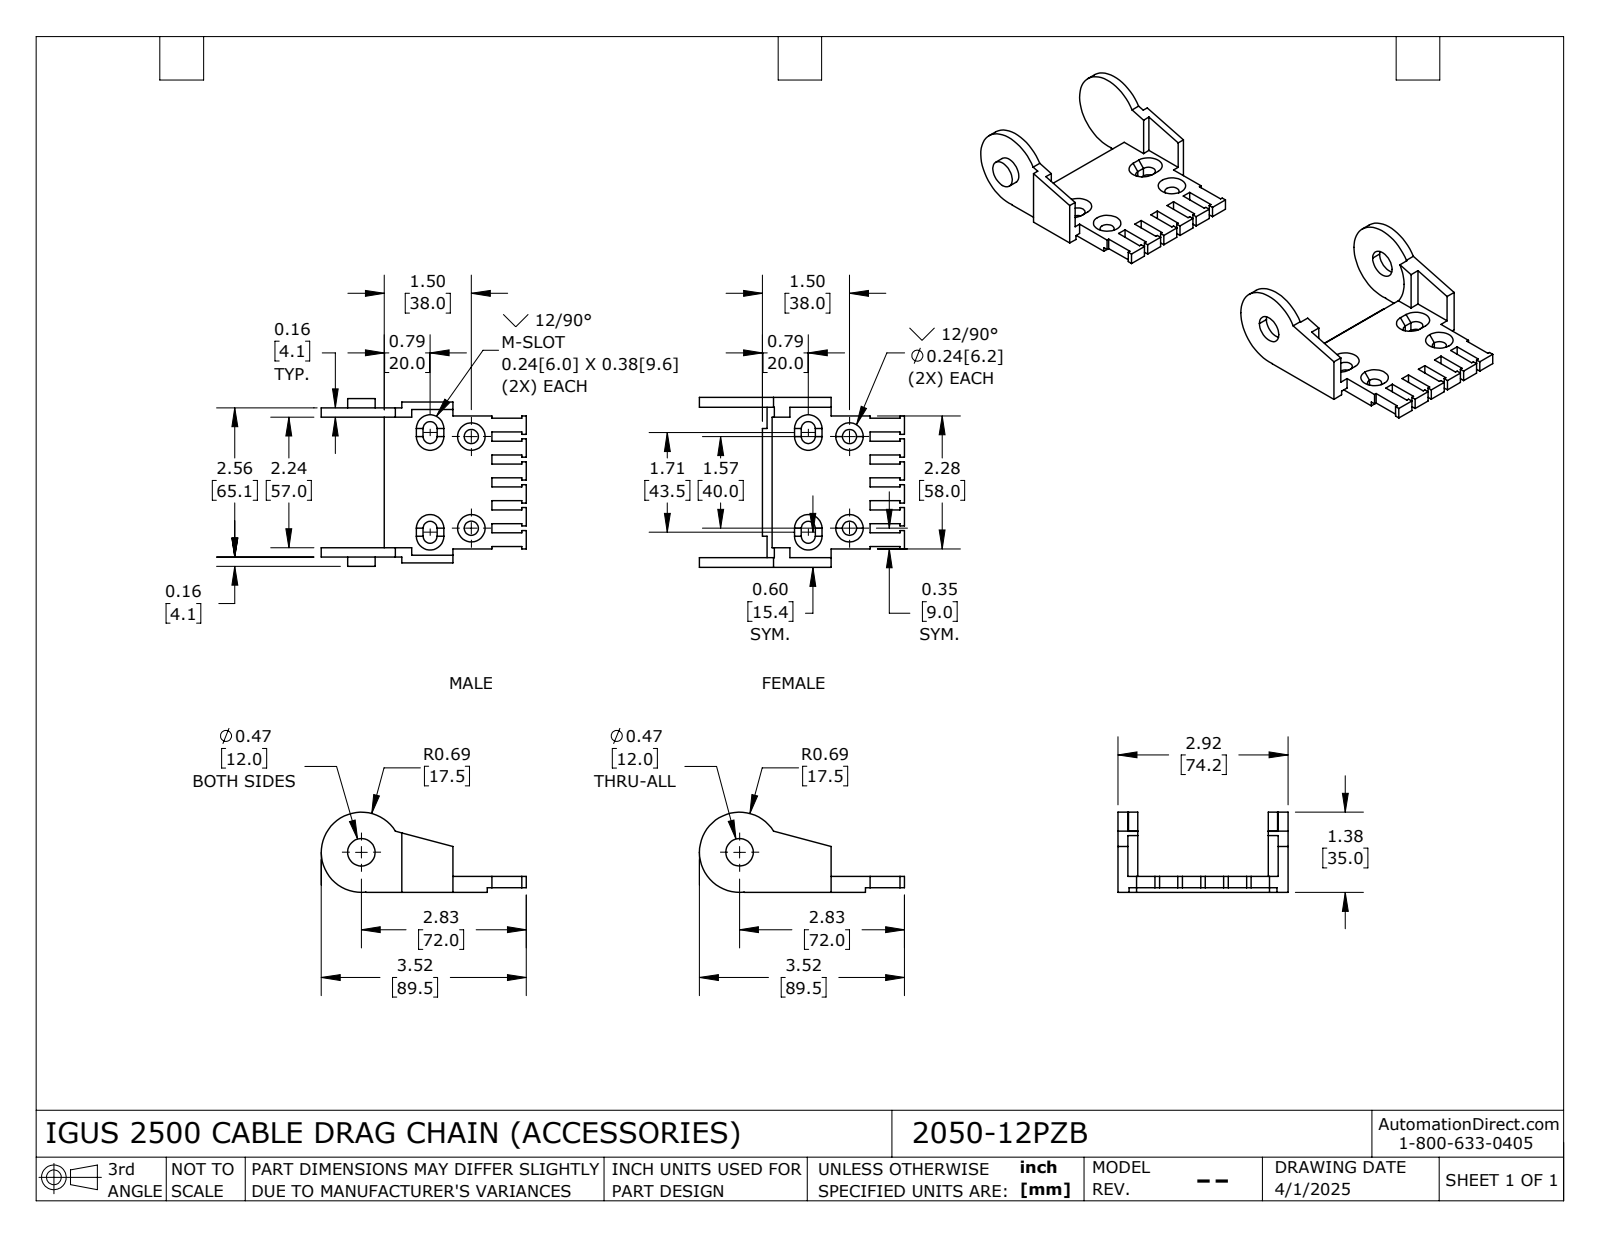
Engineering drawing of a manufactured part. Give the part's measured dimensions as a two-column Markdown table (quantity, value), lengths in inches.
| quantity | value |
| --- | --- |
| part name | 2050-12PZB |
| STEP written by | SolidWorks 2024 (AUTOMOTIVE_DESIGN) |
| units | inches |
| bodies | 2 solids, 227 faces (184 planar, 29 cylindrical, 14 other) |
| overall size | 10.024 × 2.921 × 1.378 |
| volume | 4.143 in³ |
| surface area | 53.18 in² |
| round holes (diameter × count) | 0.244 × 4, 0.472 × 1 |
| round bosses / shafts (diameter × count) | 0.472 × 1 |
| partial cylindrical surfaces (radius × count) | 0.12 × 8, 0.689 × 2, 0.697 × 1 |
| main face-to-face distances | 0.276, 0.169, 2.583, 0.079, 0.339, 2.752, 2.413, 0.179, 2.742, 2.573 |
| hole center spacings | 1.575, 6.5, 6.688 |
